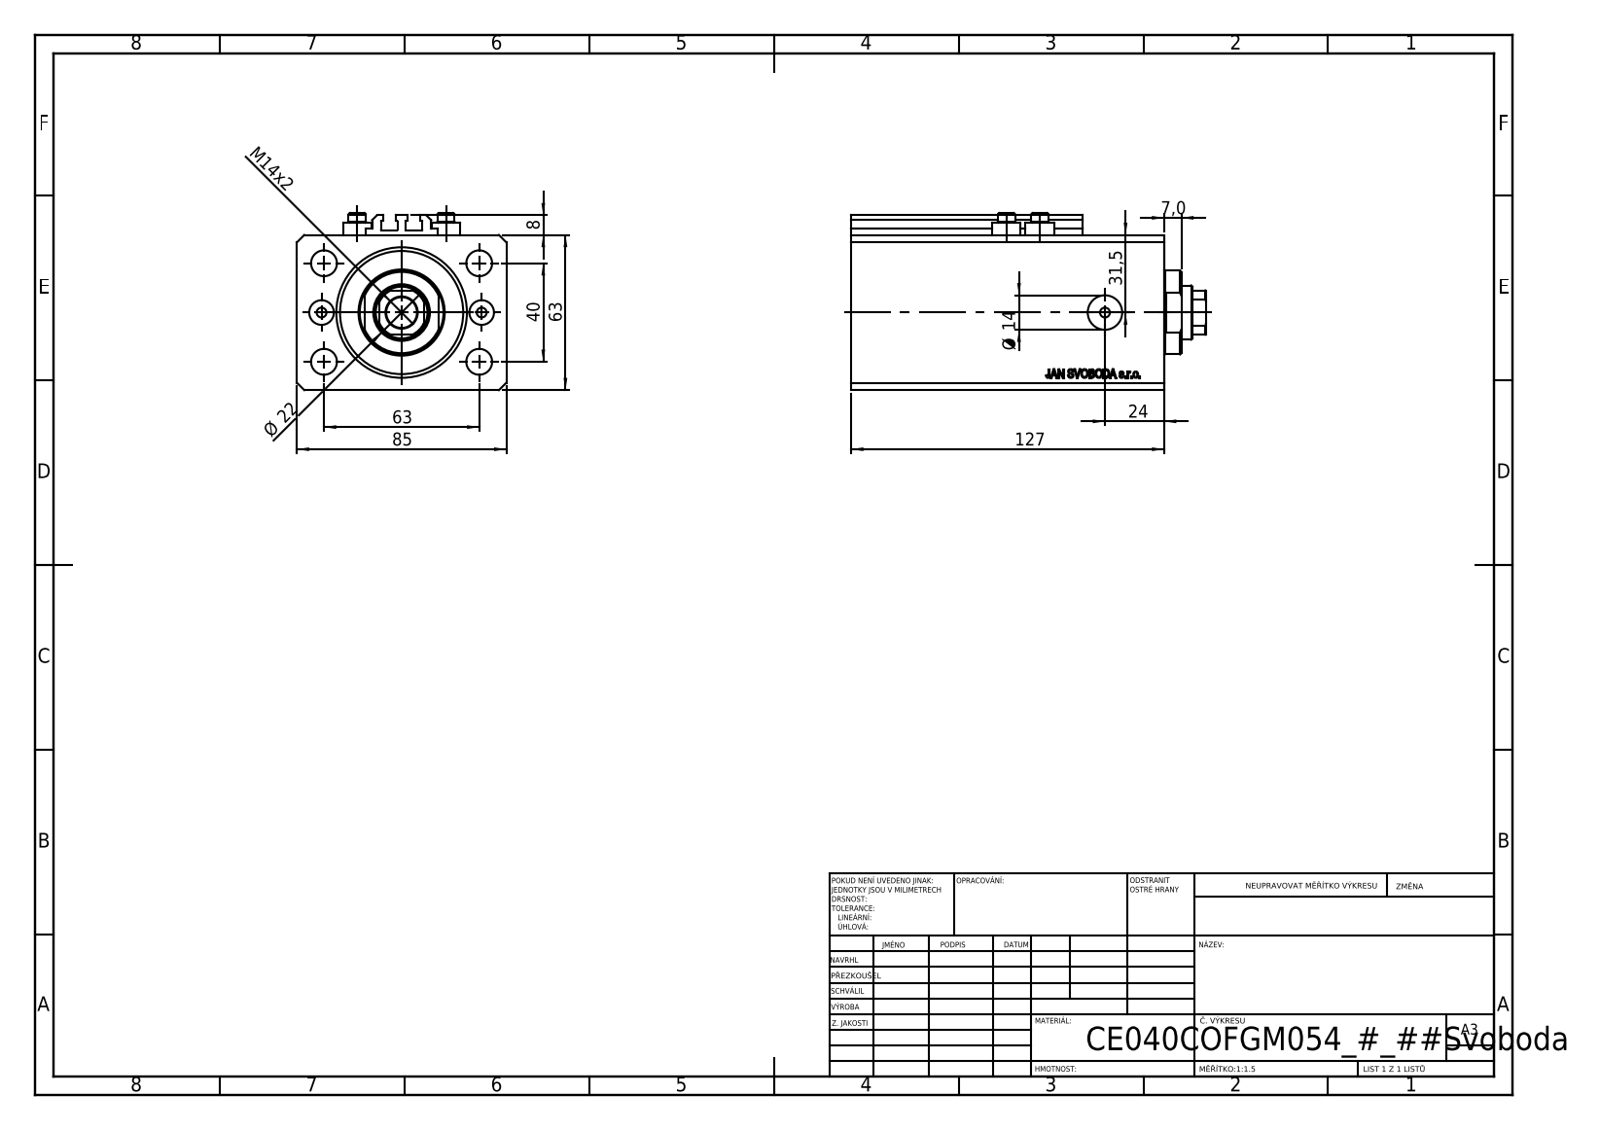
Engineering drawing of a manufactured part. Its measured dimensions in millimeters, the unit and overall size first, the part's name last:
Units: millimetres
Overall size (bounding box): 144 × 85 × 72
Round holes (diameter × count): ⌀4 ×8, ⌀10.5 ×4, ⌀10 ×2, ⌀14 ×2, ⌀12.5 ×1, ⌀22 ×1, ⌀40 ×1, ⌀53 ×1
Round bosses / shafts (diameter × count): ⌀11.6 ×4, ⌀7 ×4, ⌀34 ×1
Partial cylindrical surfaces — rounded edges, fillets, slot ends (radius × count): R0.2 ×10, R10.5 ×1
Main face-to-face distances: 63, 85, 127, 17, 110, 11.4, 98.6, 115.6, 71, 2.5
Hole centre spacings: 20.02, 37.31, 67.05, 13.6, 32.5, 36, 38.48, 40
Volume: 604 305 mm³ · Surface area: 116 554 mm²
Bodies: 8 solids, 1034 faces (504 planar, 86 cylindrical, 444 other)
Part name (STEP PRODUCT): V250CE_C_VCP; V250CE_C_Body; ALLEN BOLT V250CE; V250CE_VC_C
STEP written by: SolidWorks 2019 (CONFIG_CONTROL_DESIGN)
